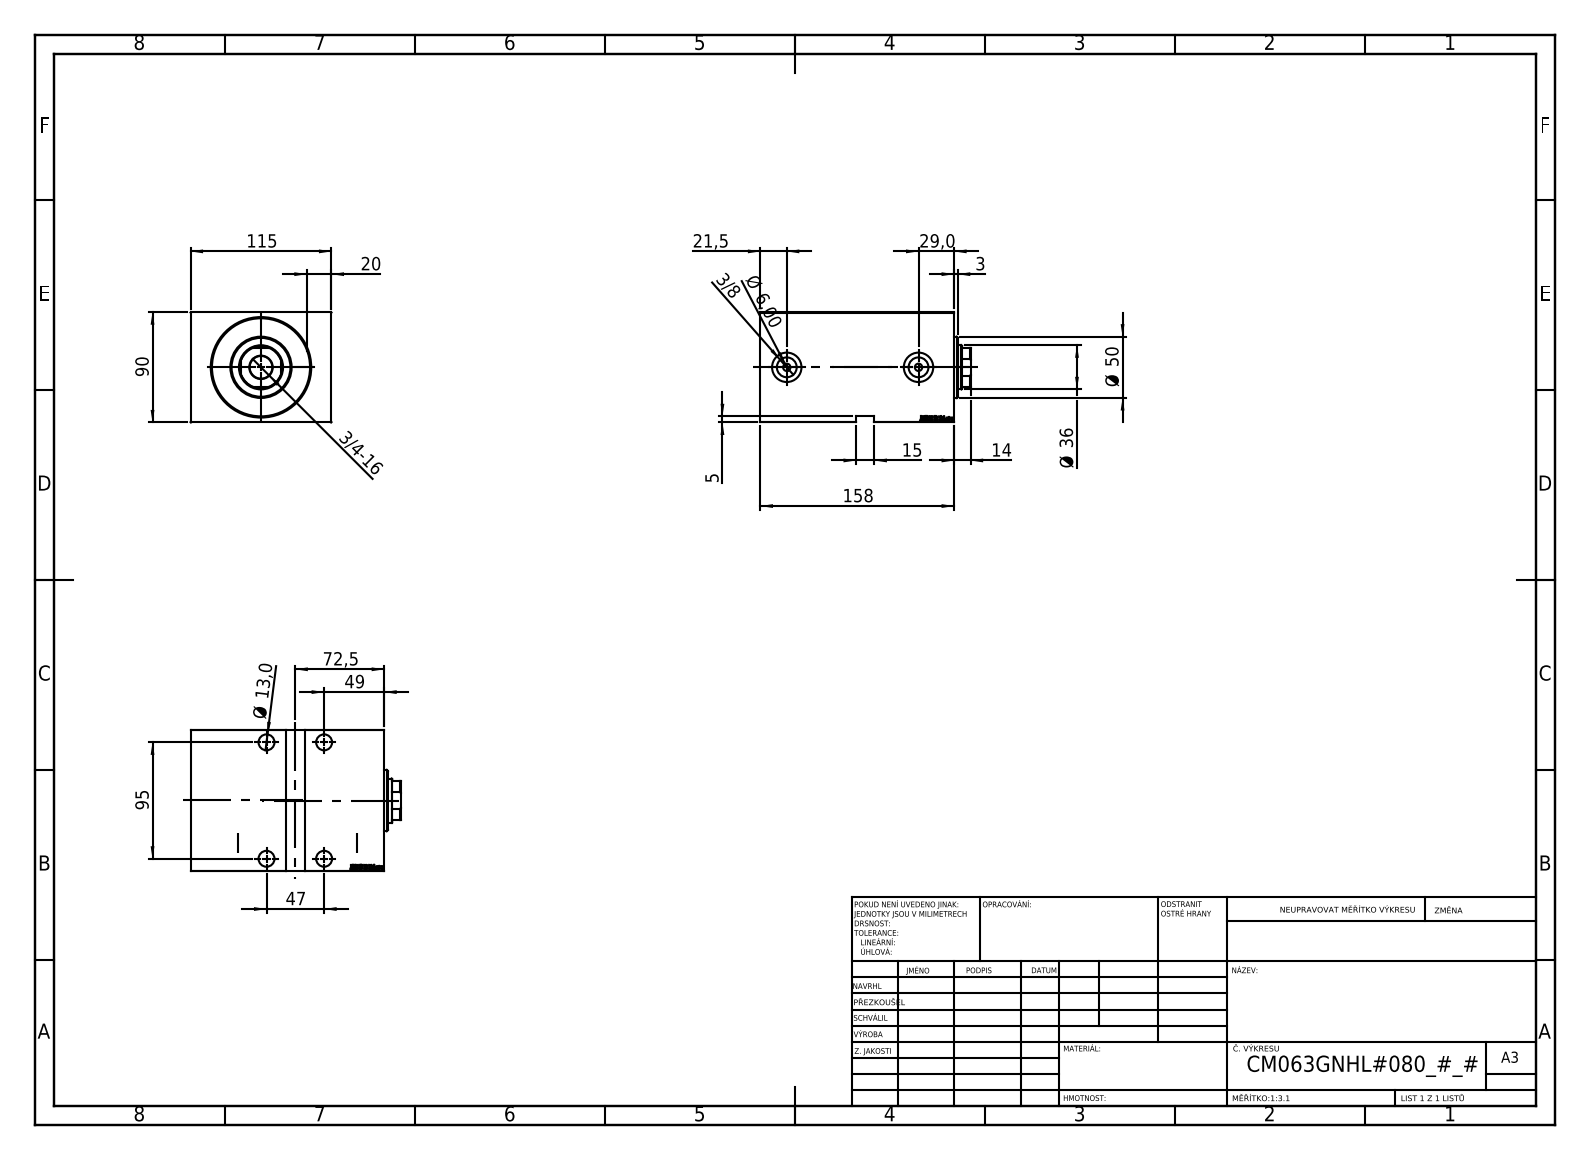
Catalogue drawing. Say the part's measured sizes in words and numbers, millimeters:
The part is named "V450CM_G_VCP; V450CM_VC_G; Zatka_OIL_PORT; V450CM_G_Body". Its 3-D file was written by "SolidWorks 2019 (CONFIG_CONTROL_DESIGN)". It is 5 solids with 891 faces: 439 planar, 54 cylindrical and 398 other. Overall it measures 171.5 by 115 by 90 millimeters. Its volume is 1 382 000 cubic millimeters and its surface area 173 587 square millimeters. Round holes: 4 of diameter 13, 4 of diameter 19, 2 of diameter 6, 2 of diameter 16.17, 2 of diameter 24, 1 of diameter 18.5, 1 of diameter 36, 1 of diameter 63, 1 of diameter 65, 1 of diameter 80. Round bosses or shafts: 2 of diameter 22, 1 of diameter 50. Partial cylindrical surfaces (rounded edges, fillets, slot ends): 1 of radius 17.5. The main face-to-face distances are 90, 115, 158, 5, 17.5, 140.5, 153, 135.5, 93.5, 88.5. The hole center spacings are 47, 95, 105.99, 107.5.
